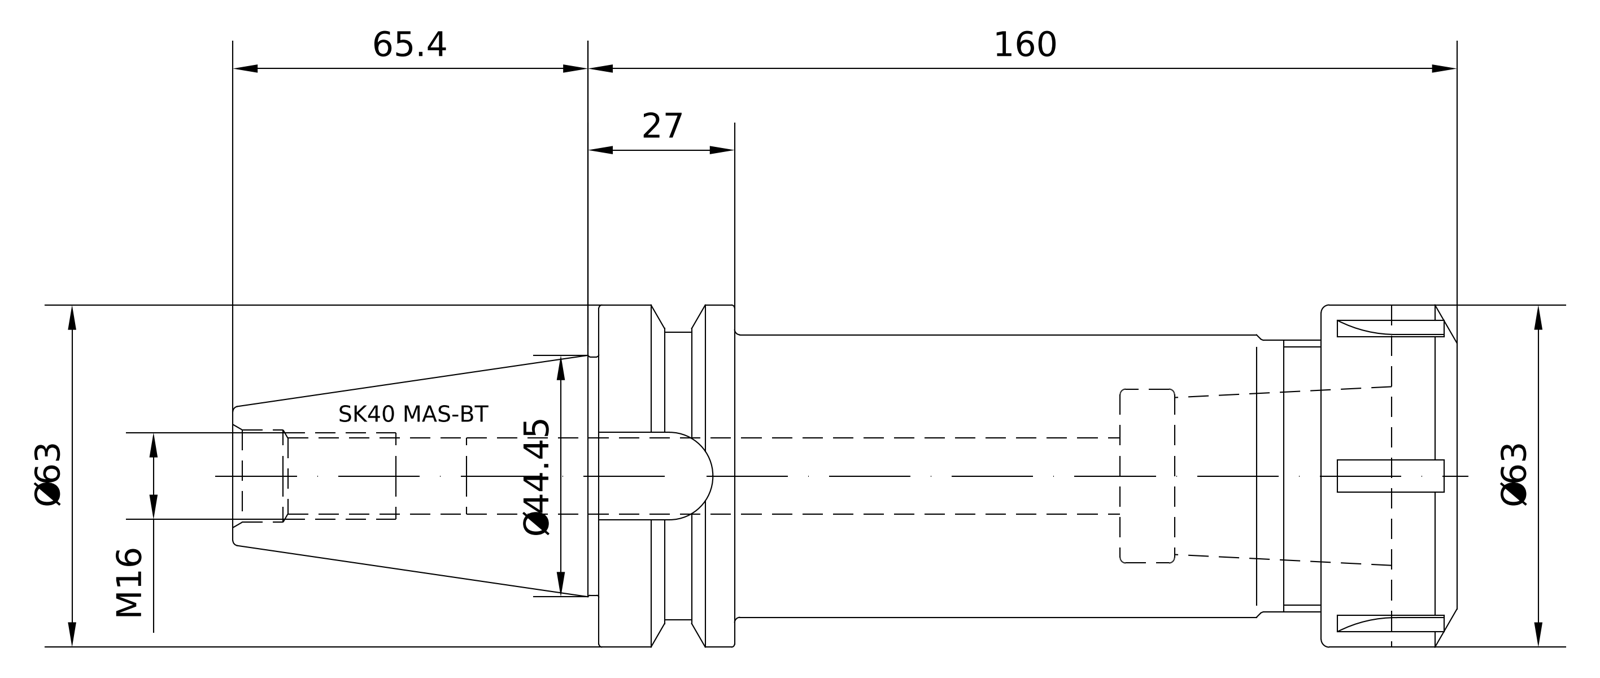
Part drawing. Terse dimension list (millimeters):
name: 40-522-40; 83-912-40; 40-522-40_ASM
written by: PRO/ENGINEER BY PARAMETRIC TECHNOLOGY CORPORATION, 2010430 (CONFIG_CONTROL_DESIGN)
unit: mm
bodies: 2 solids, 148 faces (54 planar, 32 cylindrical, 62 other)
size: 225.4 × 63 × 63
volume: 401 018 mm³; area: 56 957 mm²
holes: 1× ⌀13.84, 1× ⌀17.01, 1× ⌀17.5, 1× ⌀27
bosses: 1× ⌀63, 1× ⌀62.98, 1× ⌀52.75, 1× ⌀52, 1× ⌀50, 1× ⌀43.75, 1× ⌀16.01
rounds: 6× R2.7, 1× R8.1
face distances: 25.5, 132.5, 158, 143, 10.5, 15, 25, 107.5, 118, 133
